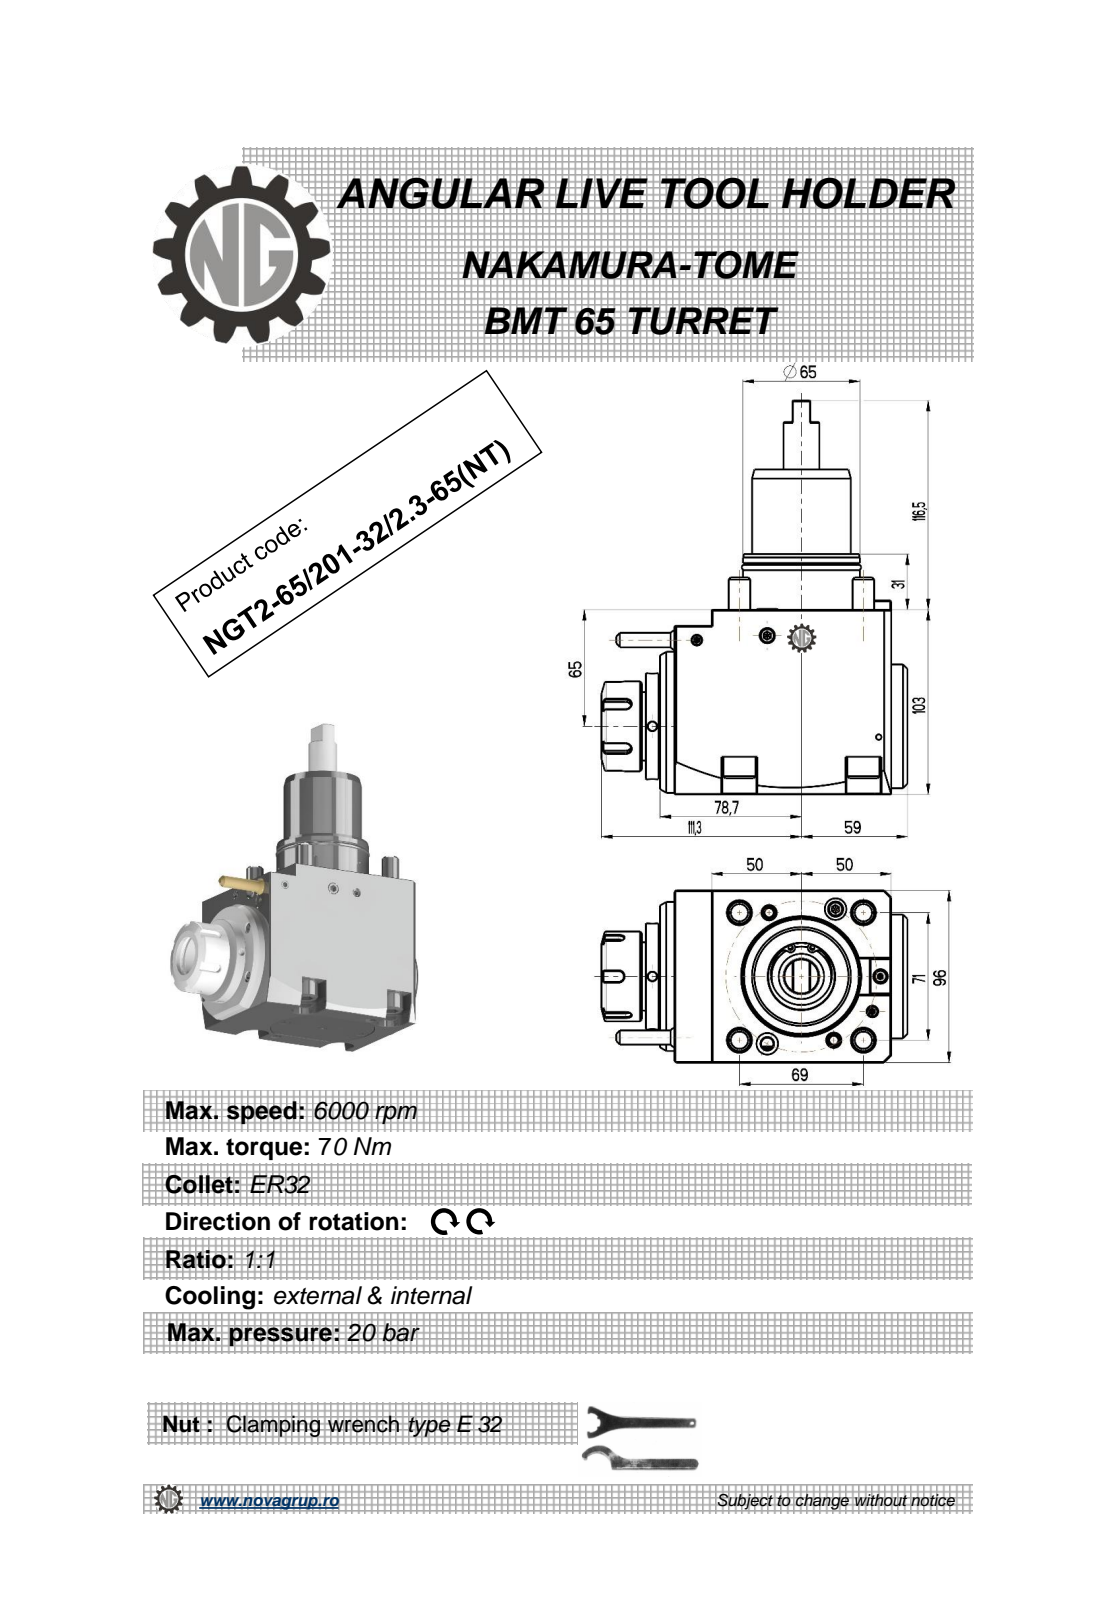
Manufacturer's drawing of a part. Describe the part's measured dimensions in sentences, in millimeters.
The part is named "NGT2_65_201_32_2_3_65_NT". Its 3-D file was written by "PRO/ENGINEER BY PARAMETRIC TECHNOLOGY CORPORATION, 2010280 (CONFIG_CONTROL_DESIGN)". It is 2 solids with 429 faces: 199 planar, 114 cylindrical and 116 other. Overall it measures 219.5 by 170.3 by 96 millimeters. Its volume is 1 520 000 cubic millimeters and its surface area 109 597 square millimeters. Round holes: 3 of diameter 5, 2 of diameter 6.8, 1 of diameter 3, 1 of diameter 12, 1 of diameter 27, 1 of diameter 46. Round bosses or shafts: 4 of diameter 18, 4 of diameter 12, 1 of diameter 83, 1 of diameter 69, 1 of diameter 65, 1 of diameter 60, 1 of diameter 59, 1 of diameter 55. Partial cylindrical surfaces (rounded edges, fillets, slot ends): 20 of radius 0.36, 6 of radius 0.22, 5 of radius 3, 4 of radius 9.5, 2 of radius 0.8, 2 of radius 550, 1 of radius 4. The main face-to-face distances are 96, 9, 103, 8, 94, 120.7, 129.7, 128.7, 137.7, 87. The hole center spacings are 58.82, 74.13, 84.08, 108.63.
